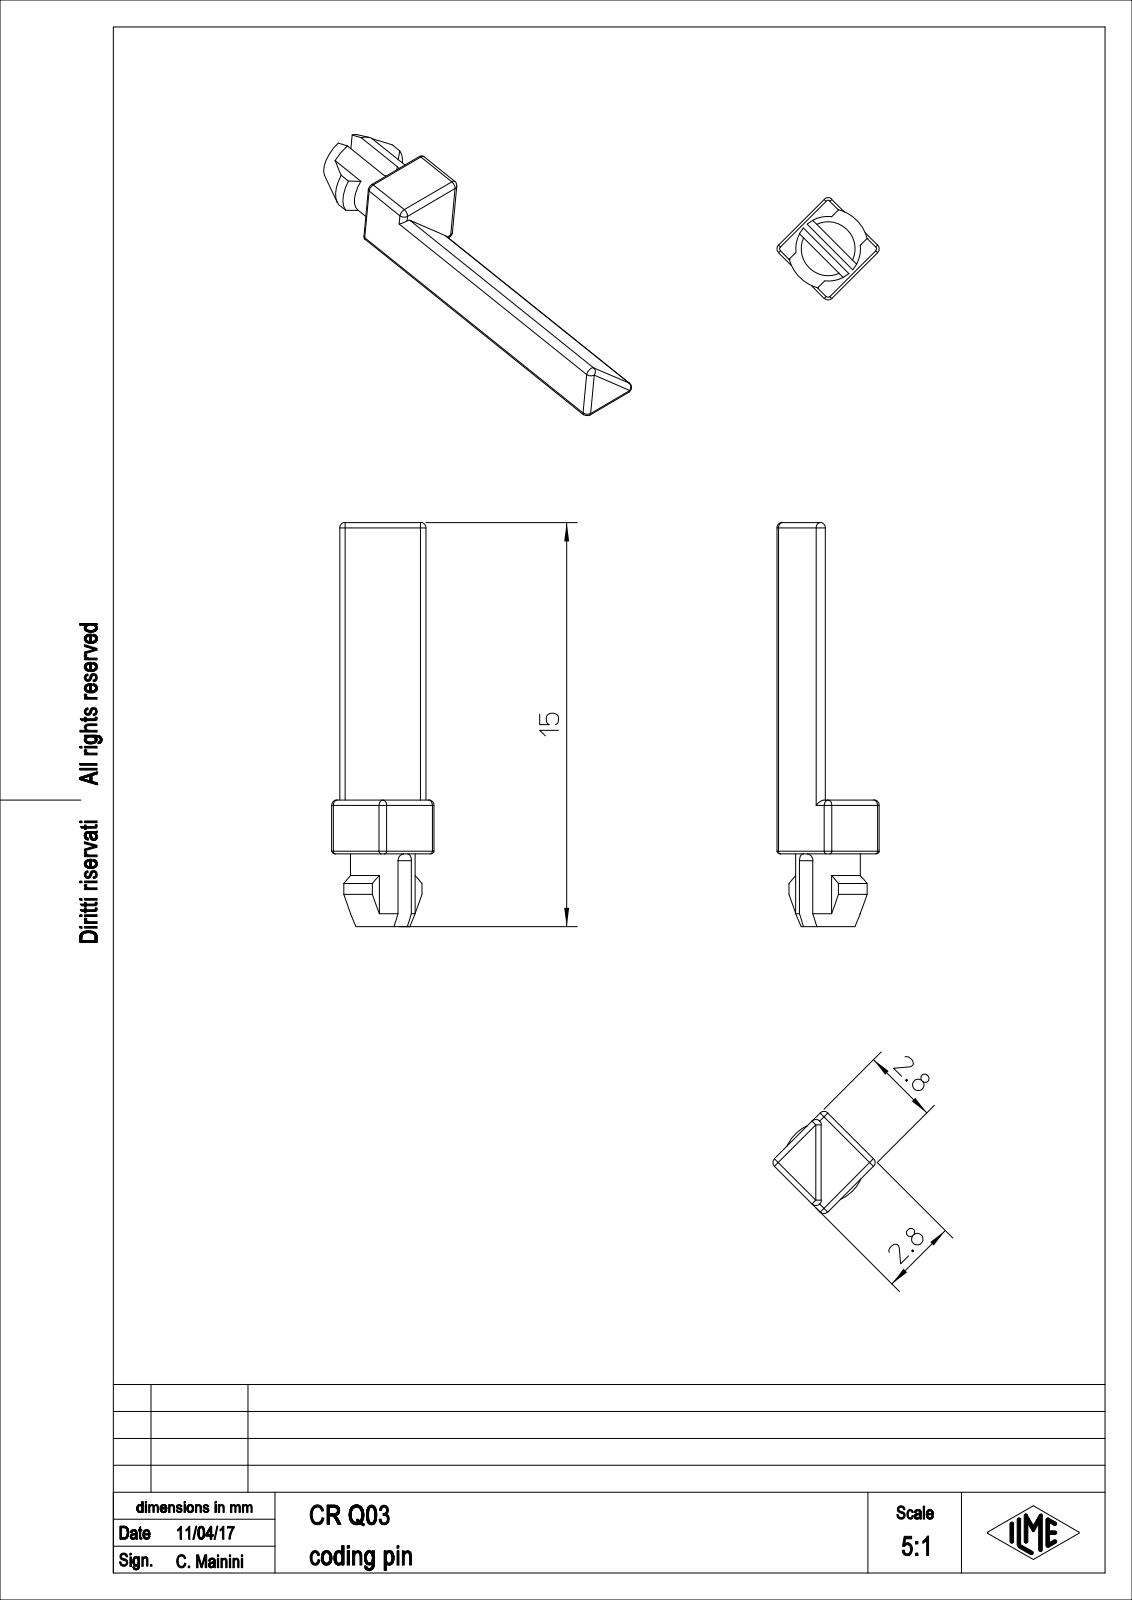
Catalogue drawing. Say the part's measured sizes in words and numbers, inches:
The part is named "CR_Q03". Its 3-D file was written by "PTC Creo Elements/Direct Modeling 19.0E 27-Jun-2016 (C) Parametric Technology GmbH (AUTOMOTIVE_DESIGN)". It is 1 solid with 54 faces: 16 planar, 23 cylindrical and 15 other. Overall it measures 0.591 by 0.149 by 0.149 inches. Its volume is 0.004 cubic inches and its surface area 0.228 square inches. Round bosses or shafts: 1 of diameter 0.094. Partial cylindrical surfaces (rounded edges, fillets, slot ends): 13 of radius 0.008, 4 of radius 0.004, 2 of radius 0.01, 1 of radius 0.059. The main face-to-face distances are 0.069, 0.041, 0.11, 0.028, 0.079, 0.484, 0.406, 0.106, 0.185, 0.591.
